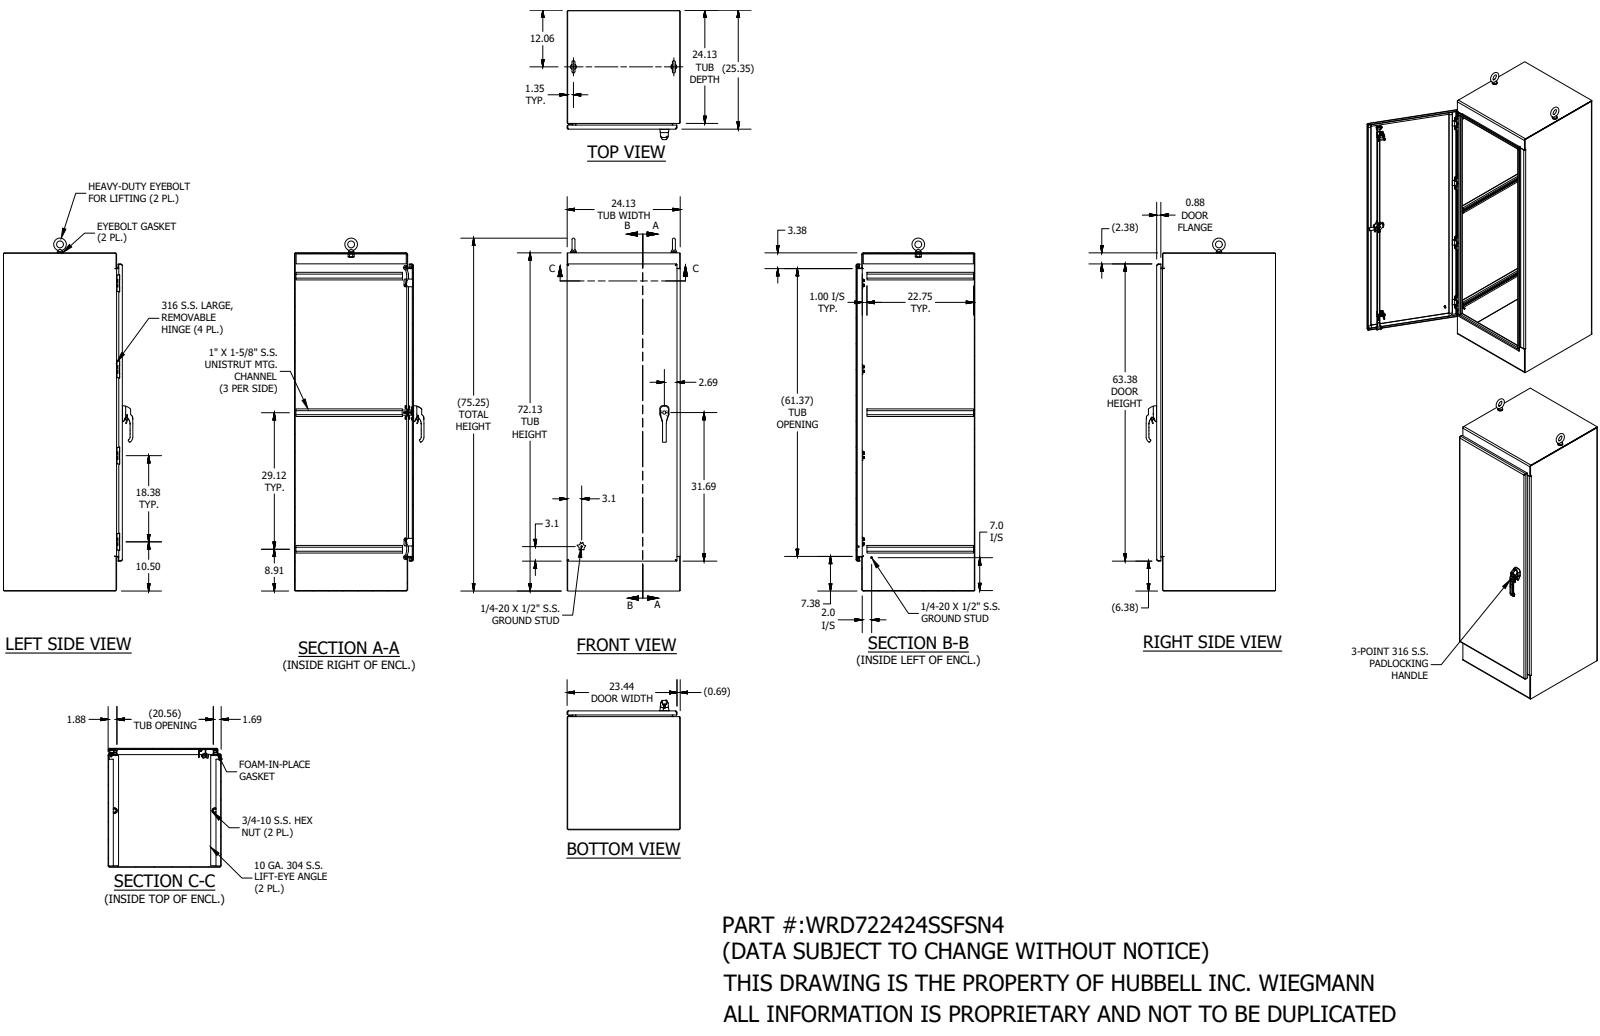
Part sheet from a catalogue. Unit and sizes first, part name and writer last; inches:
Units: inches
Overall size (bounding box): 75.248 × 27.598 × 24.129
Round holes (diameter × count): ⌀0.14 ×24, ⌀0.195 ×8, ⌀0.262 ×8, ⌀0.266 ×8, ⌀0.294 ×8, ⌀0.65 ×8, ⌀0.136 ×4, ⌀0.164 ×4, ⌀0.187 ×4, ⌀0.201 ×4, ⌀0.213 ×3, ⌀0.281 ×3
Round bosses / shafts (diameter × count): ⌀0.625 ×8, ⌀0.25 ×7, ⌀0.237 ×4, ⌀0.236 ×3, ⌀1.25 ×2, ⌀1.12 ×2, ⌀1 ×2, ⌀0.75 ×2
Partial cylindrical surfaces — rounded edges, fillets, slot ends (radius × count): R0.02 ×172, R0.012 ×114, R0.125 ×34, R0.062 ×26, R0.019 ×21, R0.05 ×14, R0.079 ×14, R0.25 ×13
Main face-to-face distances: 0.104, 24.021, 23.917, 24.125, 25.245, 25.141, 25.349, 25.245, 0.104, 72.021
Hole centre spacings: 0.018, 0.023, 0.024, 0.38, 0.76, 1, 18.375, 36.75
Volume: 1 056 in³ · Surface area: 19 683 in²
Bodies: 103 solids, 3881 faces (1580 planar, 1362 cylindrical, 939 other)
Part name (STEP PRODUCT): WRD722424SSFSN4
STEP written by: SolidWorks 2019 (AUTOMOTIVE_DESIGN)
